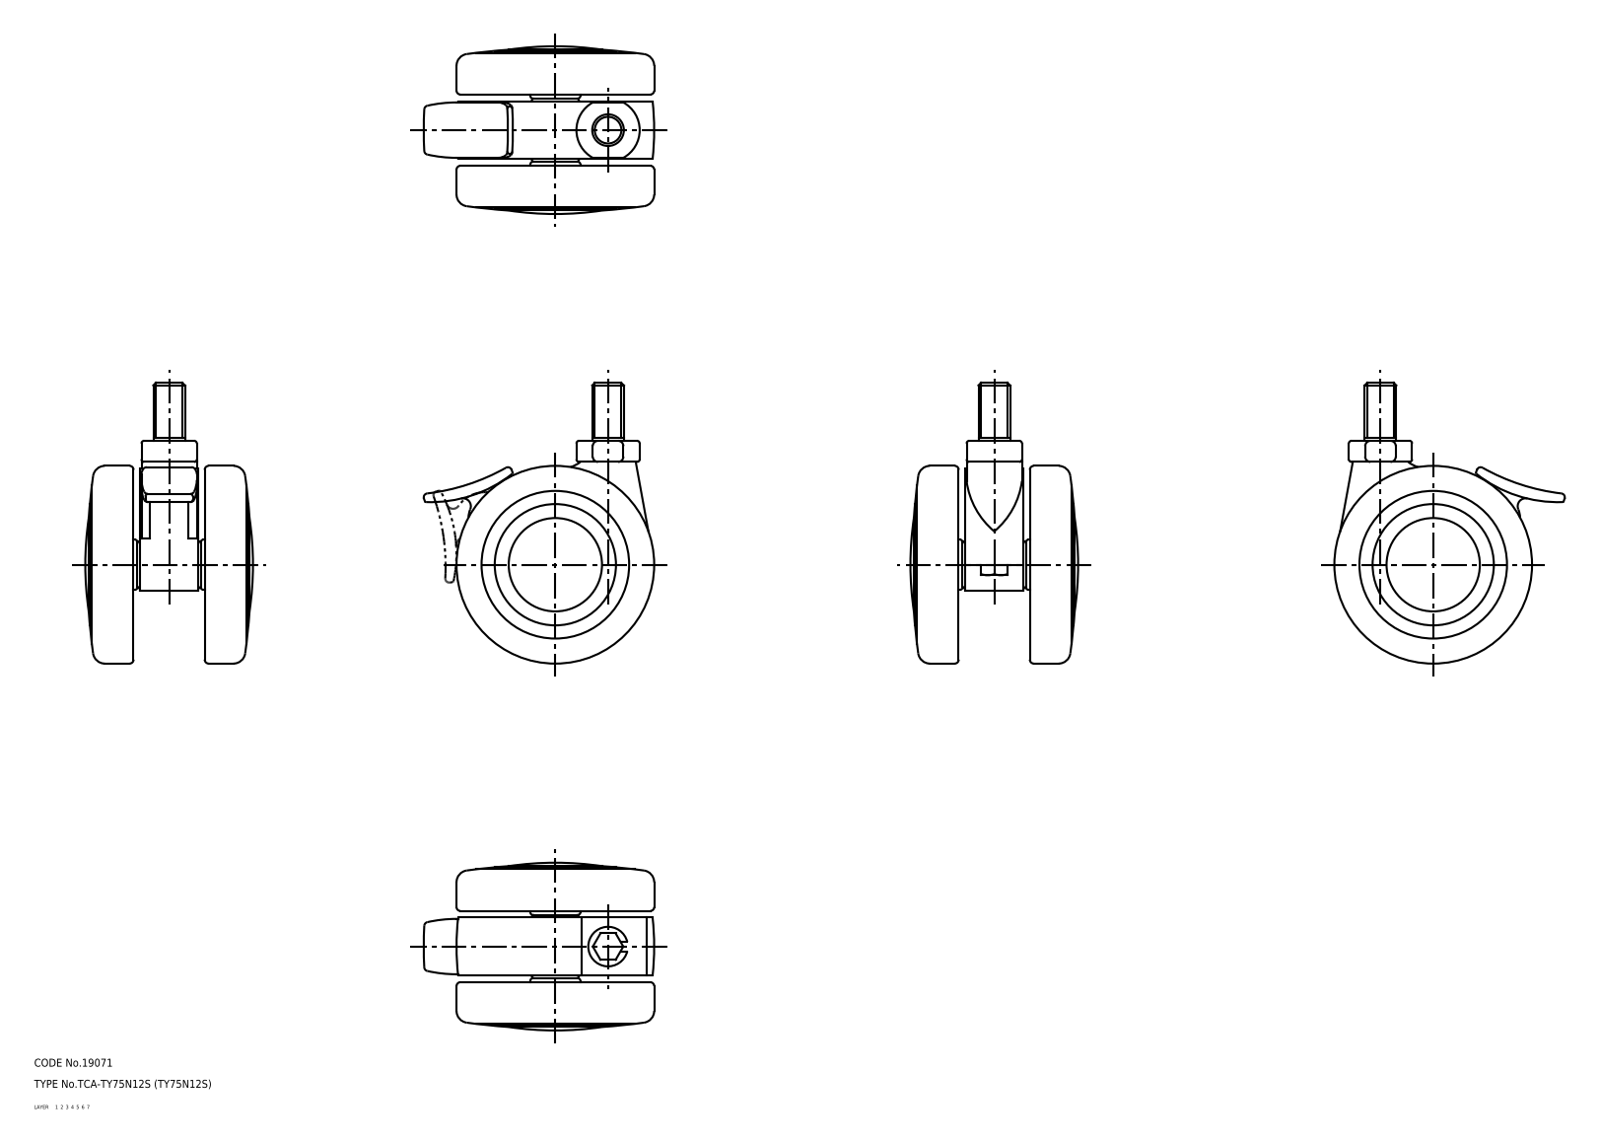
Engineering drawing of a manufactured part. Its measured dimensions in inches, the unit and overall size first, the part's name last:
Units: inches
Overall size (bounding box): 4.193 × 3.443 × 2.505
Volume: 11.61 in³ · Surface area: 81.66 in²
Bodies: 5 solids, 198 faces (0 planar, 0 cylindrical, 198 other)
Part name (STEP PRODUCT): lever; wheel_mr; wheel; main shaft (+1 more)
STEP written by: CADfix (AUTOMOTIVE_DESIGN)
